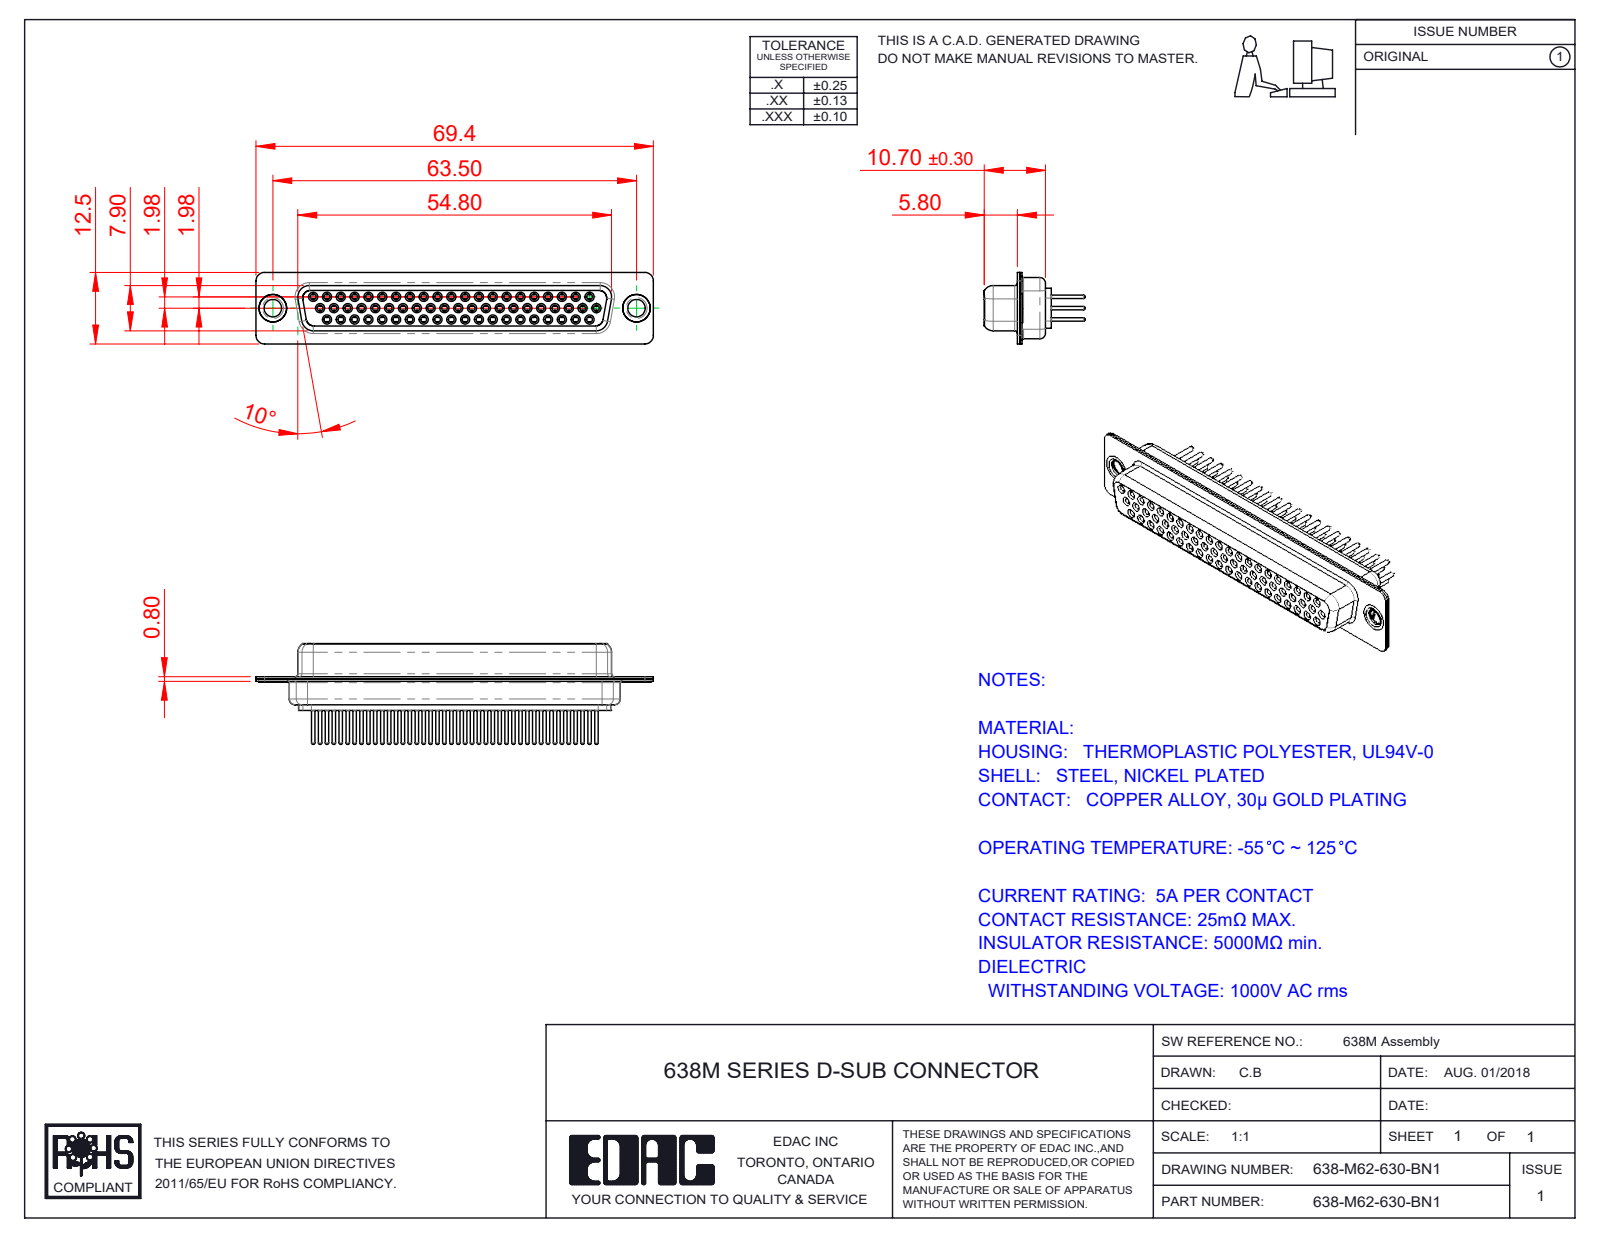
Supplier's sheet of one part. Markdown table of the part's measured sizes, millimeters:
| quantity | value |
| --- | --- |
| part name | 638M Housing_62 Contacts; 638M Shell Front_62 Contacts; 638M Thru Hole Rivet; 638M Contact Row 1_30 (+4 more) |
| STEP written by | SolidWorks 2020 (CONFIG_CONTROL_DESIGN) |
| units | millimeters |
| bodies | 67 solids, 3663 faces (997 planar, 1299 cylindrical, 1367 other) |
| overall size | 69.4 × 17.6 × 12.5 |
| volume | 4 904 mm³ |
| surface area | 16 294 mm² |
| round holes (diameter × count) | 1 × 62, 1.1 × 62, 1.7 × 62, 1.8 × 62, 2 × 62, 3.05 × 2, 4 × 2, 4.8 × 2 |
| round bosses / shafts (diameter × count) | 2.2 × 62, 1.6 × 62, 1.5 × 62, 0.6 × 62, 5 × 2, 4.9 × 2, 3.55 × 2 |
| partial cylindrical surfaces (radius × count) | 1.5 × 16, 2 × 12, 1.35 × 8, 1.6 × 8, 0.25 × 4, 0.5 × 4, 0.6 × 4, 0.65 × 4 |
| main face-to-face distances | 0.4, 1.4, 0.45, 8.45, 8.9, 1.8, 1, 6.2, 7.05, 1.85 |
| hole center spacings | 7.24, 2.32, 2.41, 4.13, 9.65, 4.83, 14.48, 16.89 |
